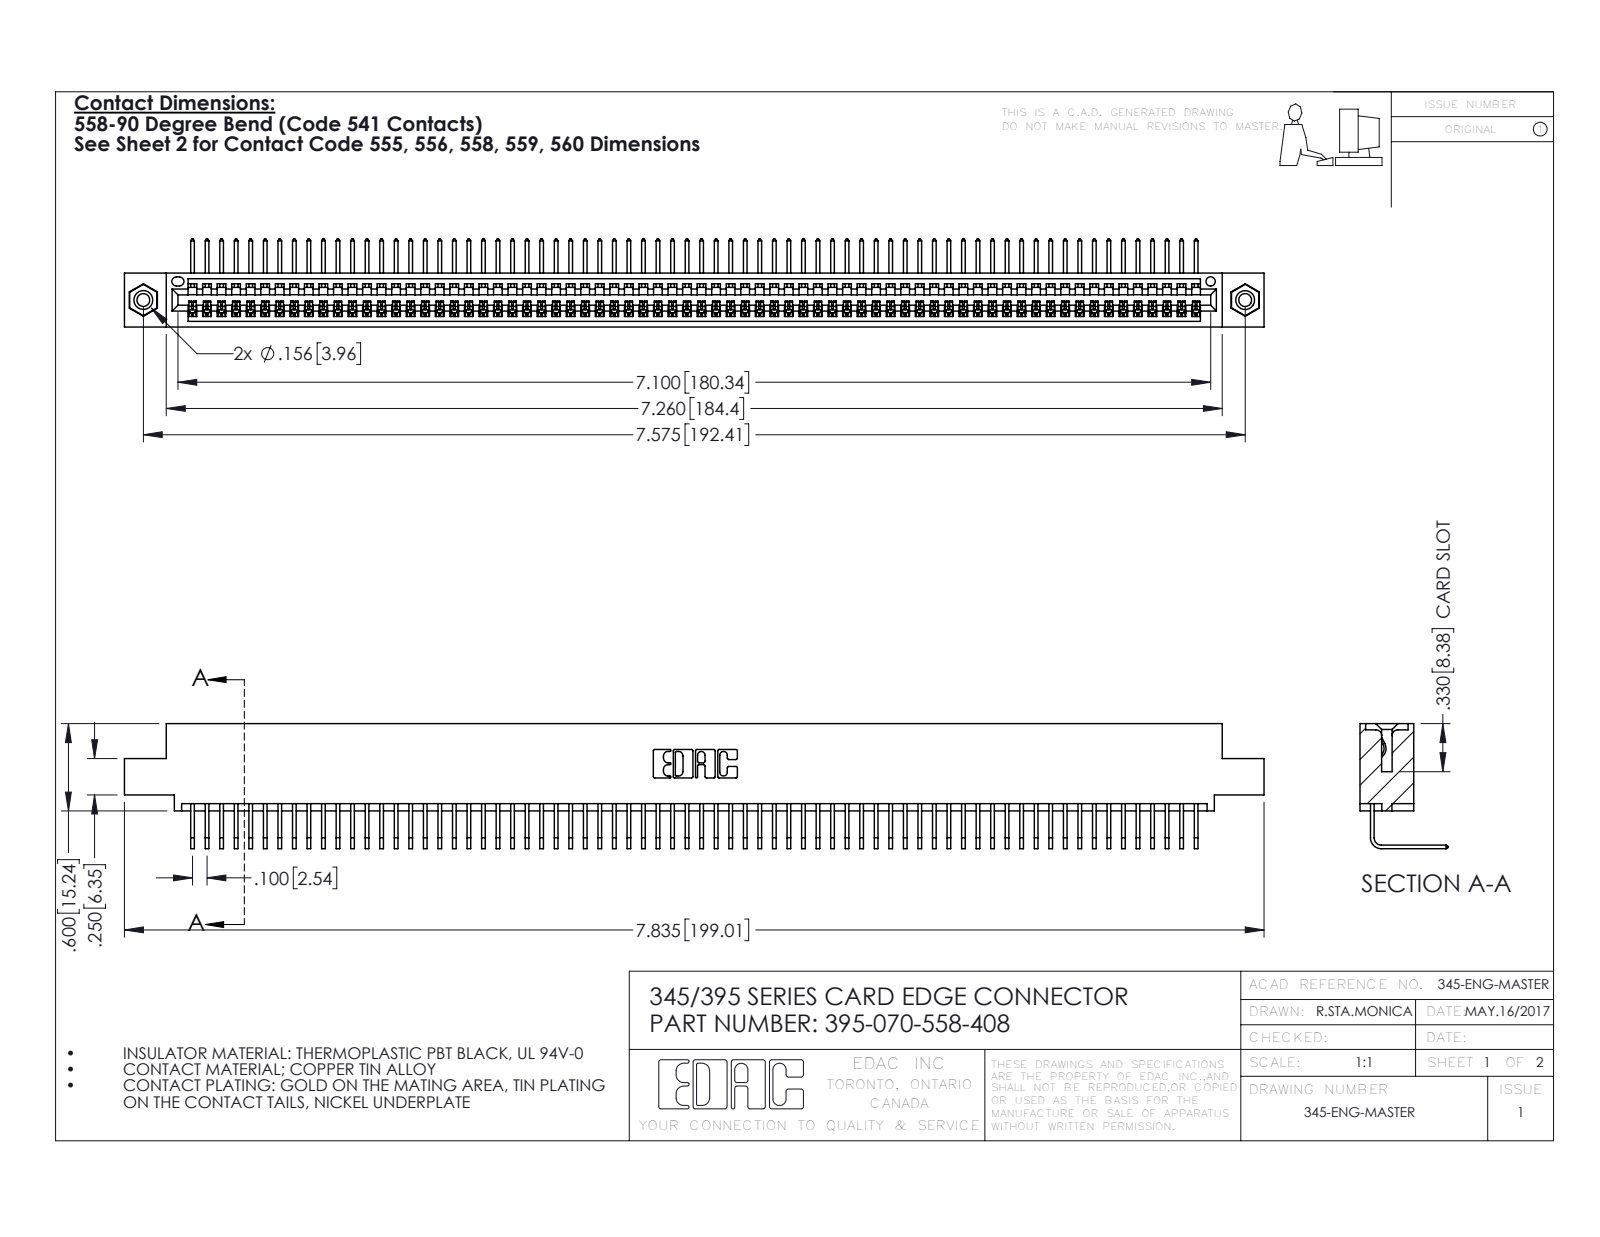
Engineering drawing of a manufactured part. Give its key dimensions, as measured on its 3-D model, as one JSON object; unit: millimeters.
{"part_name": "395-070-558-408; 345 Part_0.110 Offset - 0.156 Dia-TI; 345-292-001_558 Tail - 2; 345-250-001_345-250-003-102", "step_written_by": "SolidWorks 2016 (CONFIG_CONTROL_DESIGN)", "units": "millimeters", "bodies": {"solids": 73, "faces": 4390, "planar": 3056, "cylindrical": 1318, "other": 16}, "overall_size": [199, 21.8, 15.4], "volume_mm3": 19290, "surface_area_mm2": 27480, "round_holes": [[2.3, 2], [3.2, 2], [4, 2], [1.6, 1]], "round_bosses_or_shafts": [[3.9, 2]], "partial_cylinders_radius": [[0.2, 140], [0.3, 22], [0.2, 6], [0.8, 6], [0.7, 3], [0.8, 2], [1, 2], [0.4, 1]], "face_to_face_distances": [1.8, 7.6, 9.4, 5.1, 2.5, 6.9, 0.6, 5.7, 3.8, 1.8], "hole_center_spacings": [6.9, 186.4, 192.4]}
